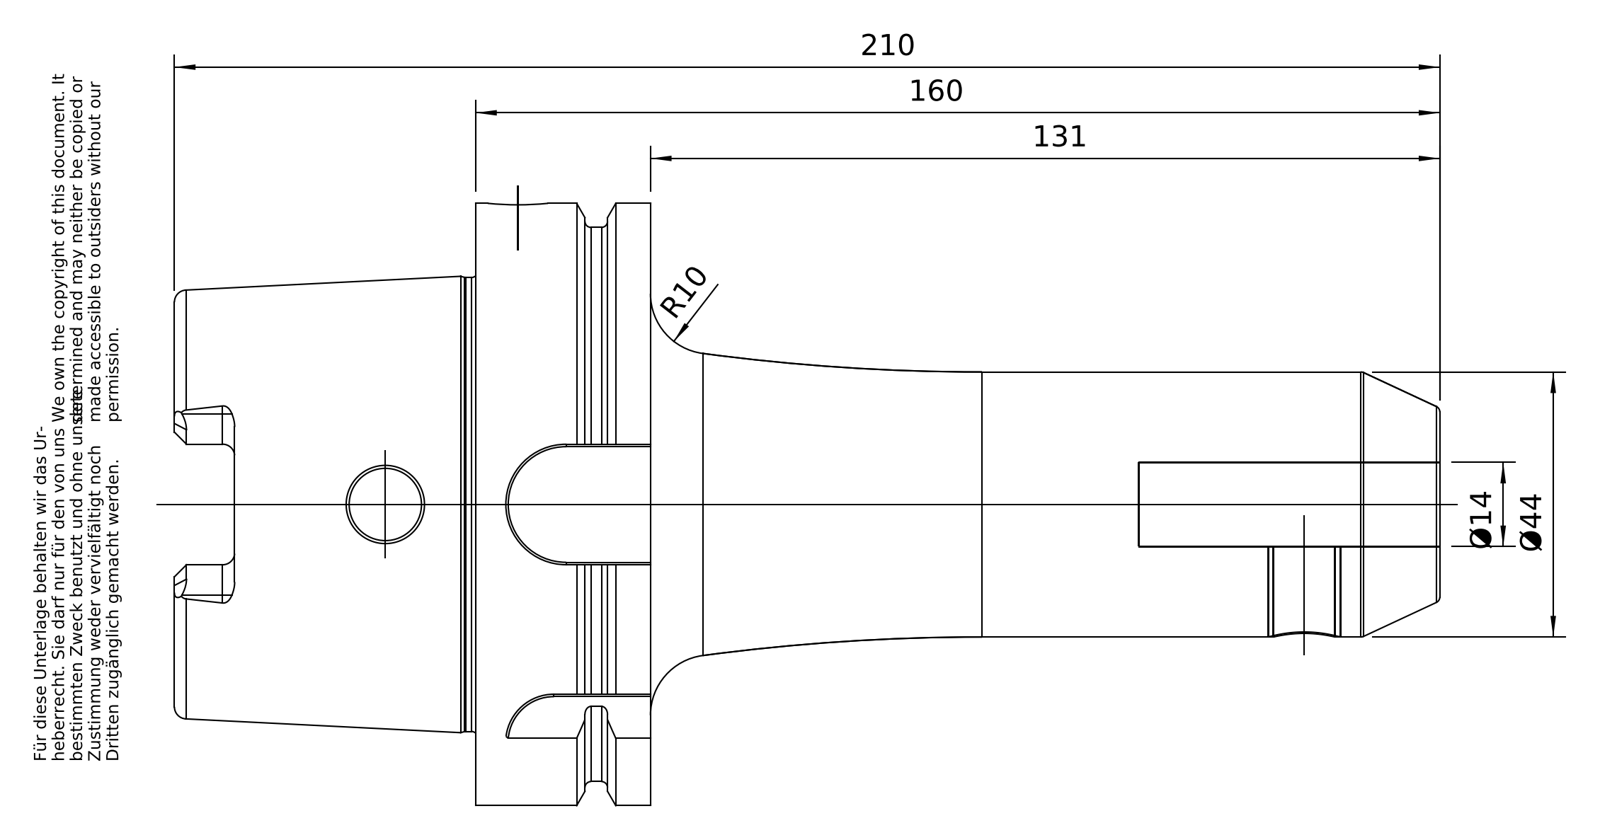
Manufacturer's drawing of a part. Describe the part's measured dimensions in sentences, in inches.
The part is named "A100-002-14". Its 3-D file was written by "PRO/ENGINEER BY PARAMETRIC TECHNOLOGY CORPORATION, 2010430 (CONFIG_CONTROL_DESIGN)". It is 1 solid with 182 faces: 50 planar, 55 cylindrical and 77 other. Overall it measures 8.268 by 3.937 by 3.937 inches. Its volume is 27.7 cubic inches and its surface area 108.6 square inches. Round holes: 2 of diameter 0.472, 1 of diameter 0.394, 1 of diameter 0.402, 1 of diameter 0.551, 1 of diameter 0.886, 1 of diameter 0.945, 1 of diameter 0.957, 1 of diameter 0.965, 1 of diameter 2.087, 1 of diameter 2.48. Round bosses or shafts: 1 of diameter 3.937, 1 of diameter 3.622, 1 of diameter 2.967, 1 of diameter 1.732. Partial cylindrical surfaces (rounded edges, fillets, slot ends): 6 of radius 0.079, 4 of radius 0.197, 1 of radius 0.315, 1 of radius 0.394, 1 of radius 0.433. The main face-to-face distances are 1.142, 0.492, 0.65, 1.969, 2.461, 3.11, 6.299, 8.268, 5.807, 5.157. The hole center spacings are 5.138.
